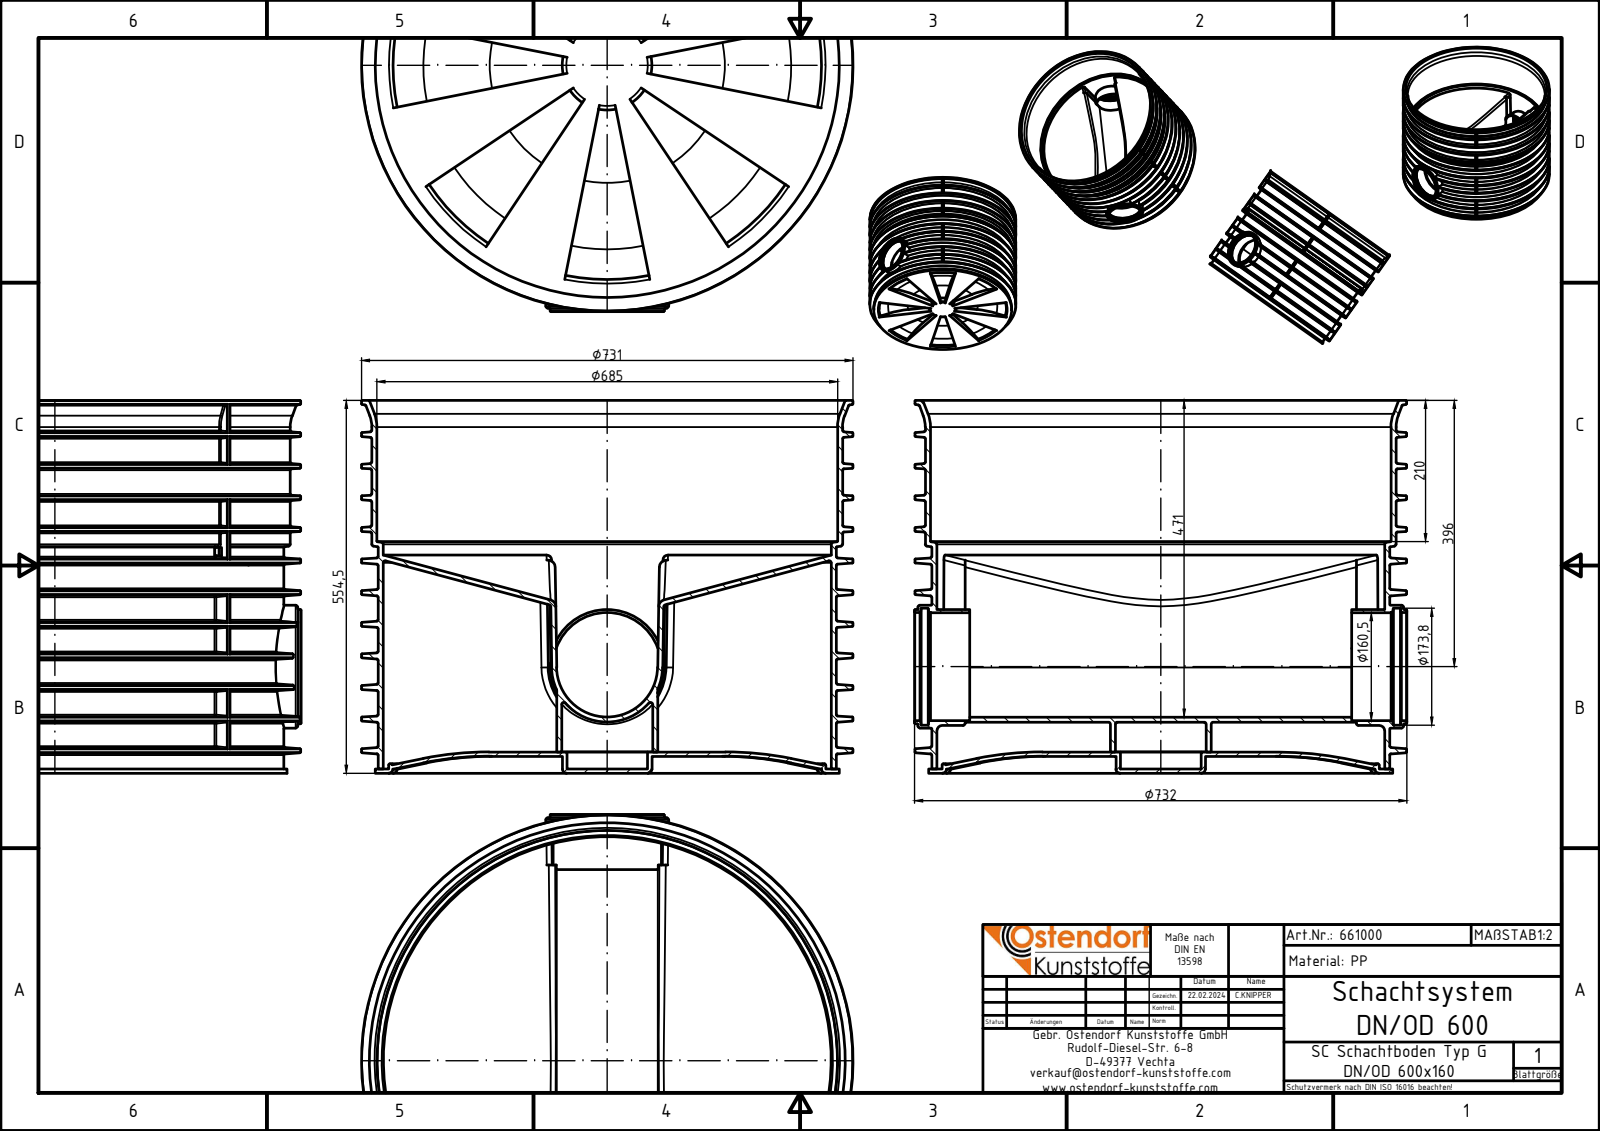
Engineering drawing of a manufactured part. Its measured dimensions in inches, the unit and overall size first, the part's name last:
Units: inches
Overall size (bounding box): 28.819 × 28.78 × 21.831
Round holes (diameter × count): ⌀4.724 ×1, ⌀5.315 ×1, ⌀6.319 ×1, ⌀6.327 ×1, ⌀6.331 ×1, ⌀6.685 ×1, ⌀6.843 ×1, ⌀25.197 ×1, ⌀26.22 ×1, ⌀26.969 ×1
Round bosses / shafts (diameter × count): ⌀28.78 ×1, ⌀27.559 ×1, ⌀27.165 ×1, ⌀26.811 ×1, ⌀25.591 ×1, ⌀7.197 ×1, ⌀6.673 ×1, ⌀5.906 ×1
Partial cylindrical surfaces — rounded edges, fillets, slot ends (radius × count): R0.079 ×16, R0.039 ×8, R0.118 ×4, R2.618 ×1, R2.953 ×1, R3.248 ×1, R3.445 ×1, R12.539 ×1
Main face-to-face distances: 0.256, 0.984, 1.24, 0.292, 0.298, 0.728, 21.831, 21.575, 20.846, 20.591
Volume: 1 407 in³ · Surface area: 8 452 in²
Bodies: 2 solids, 1627 faces (170 planar, 281 cylindrical, 1176 other)
Part name (STEP PRODUCT): 661000z; Schachtboden DN600x; Schacht DN600 Teil2
STEP written by: Autodesk Inventor 2024 (AUTOMOTIVE_DESIGN)
